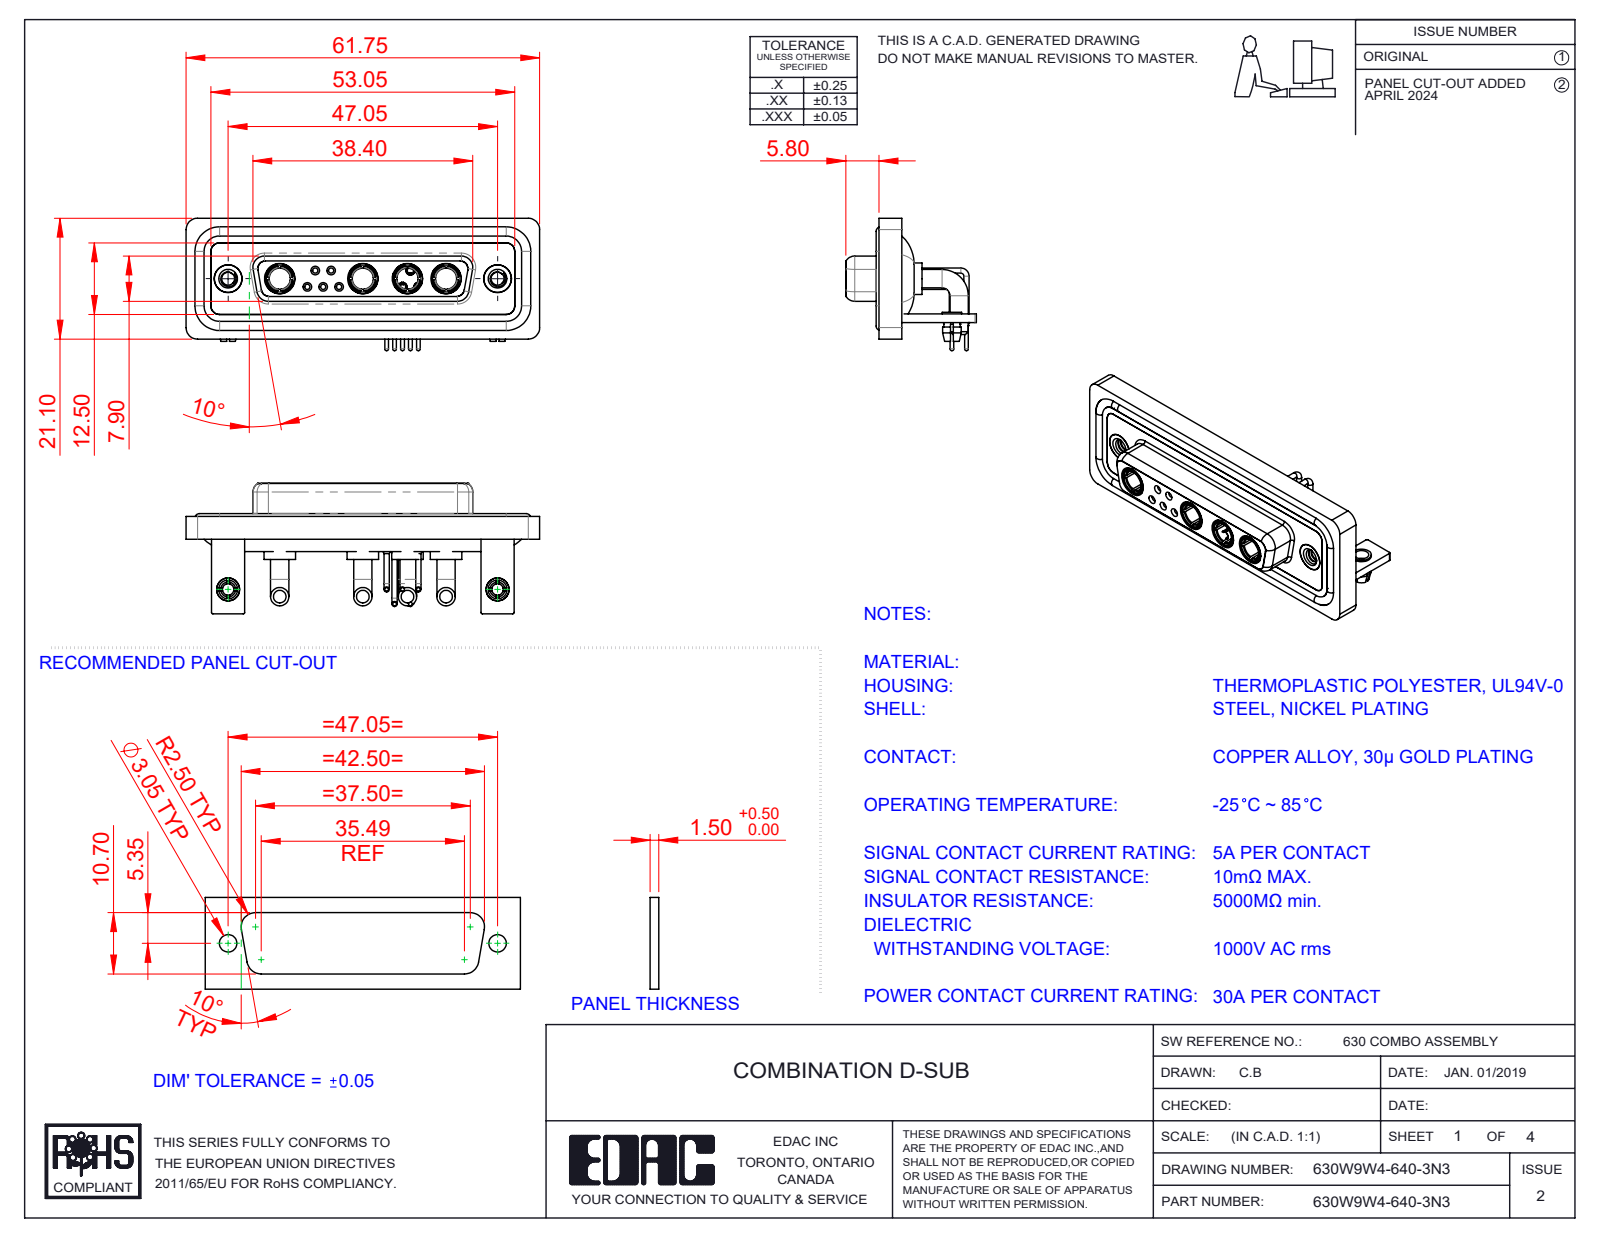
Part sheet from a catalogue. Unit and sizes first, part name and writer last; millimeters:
Units: millimetres
Overall size (bounding box): 61.75 × 23.12 × 22.8
Round holes (diameter × count): ⌀2 ×7, ⌀4.85 ×6, ⌀0.9 ×5, ⌀1.1 ×5, ⌀1.5 ×5, ⌀3.7 ×4, ⌀5.3 ×4, ⌀1.6 ×3, ⌀1.7 ×2, ⌀2.26 ×2, ⌀2.5 ×2, ⌀3.2 ×2
Round bosses / shafts (diameter × count): ⌀0.9 ×10, ⌀1.6 ×9, ⌀3.2 ×8, ⌀2 ×5, ⌀1.5 ×5, ⌀0.65 ×5, ⌀5.5 ×4, ⌀5.2 ×4
Partial cylindrical surfaces — rounded edges, fillets, slot ends (radius × count): R2 ×19, R1.5 ×18, R0.25 ×16, R1.35 ×8, R1.6 ×8, R0.5 ×5, R0.6 ×4, R0.65 ×4
Main face-to-face distances: 0.4, 1.8, 2.9, 3.7, 1.5, 4.1, 1.1, 1.4, 1.6, 2.5
Hole centre spacings: 3.16, 2.77, 5.04, 13.85, 11.08, 12.79, 15.5, 5.54
Volume: 8 966 mm³ · Surface area: 15 066 mm²
Bodies: 24 solids, 1103 faces (364 planar, 459 cylindrical, 280 other)
Part name (STEP PRODUCT): 630W9W4-640-3N3; 630Combo Contact Row 2_50 Contacts; 630Combo Stabilizer Bracket_50 Contacts; 630Combo Housing_9W4 (+7 more)
STEP written by: SolidWorks 2023 (CONFIG_CONTROL_DESIGN)
